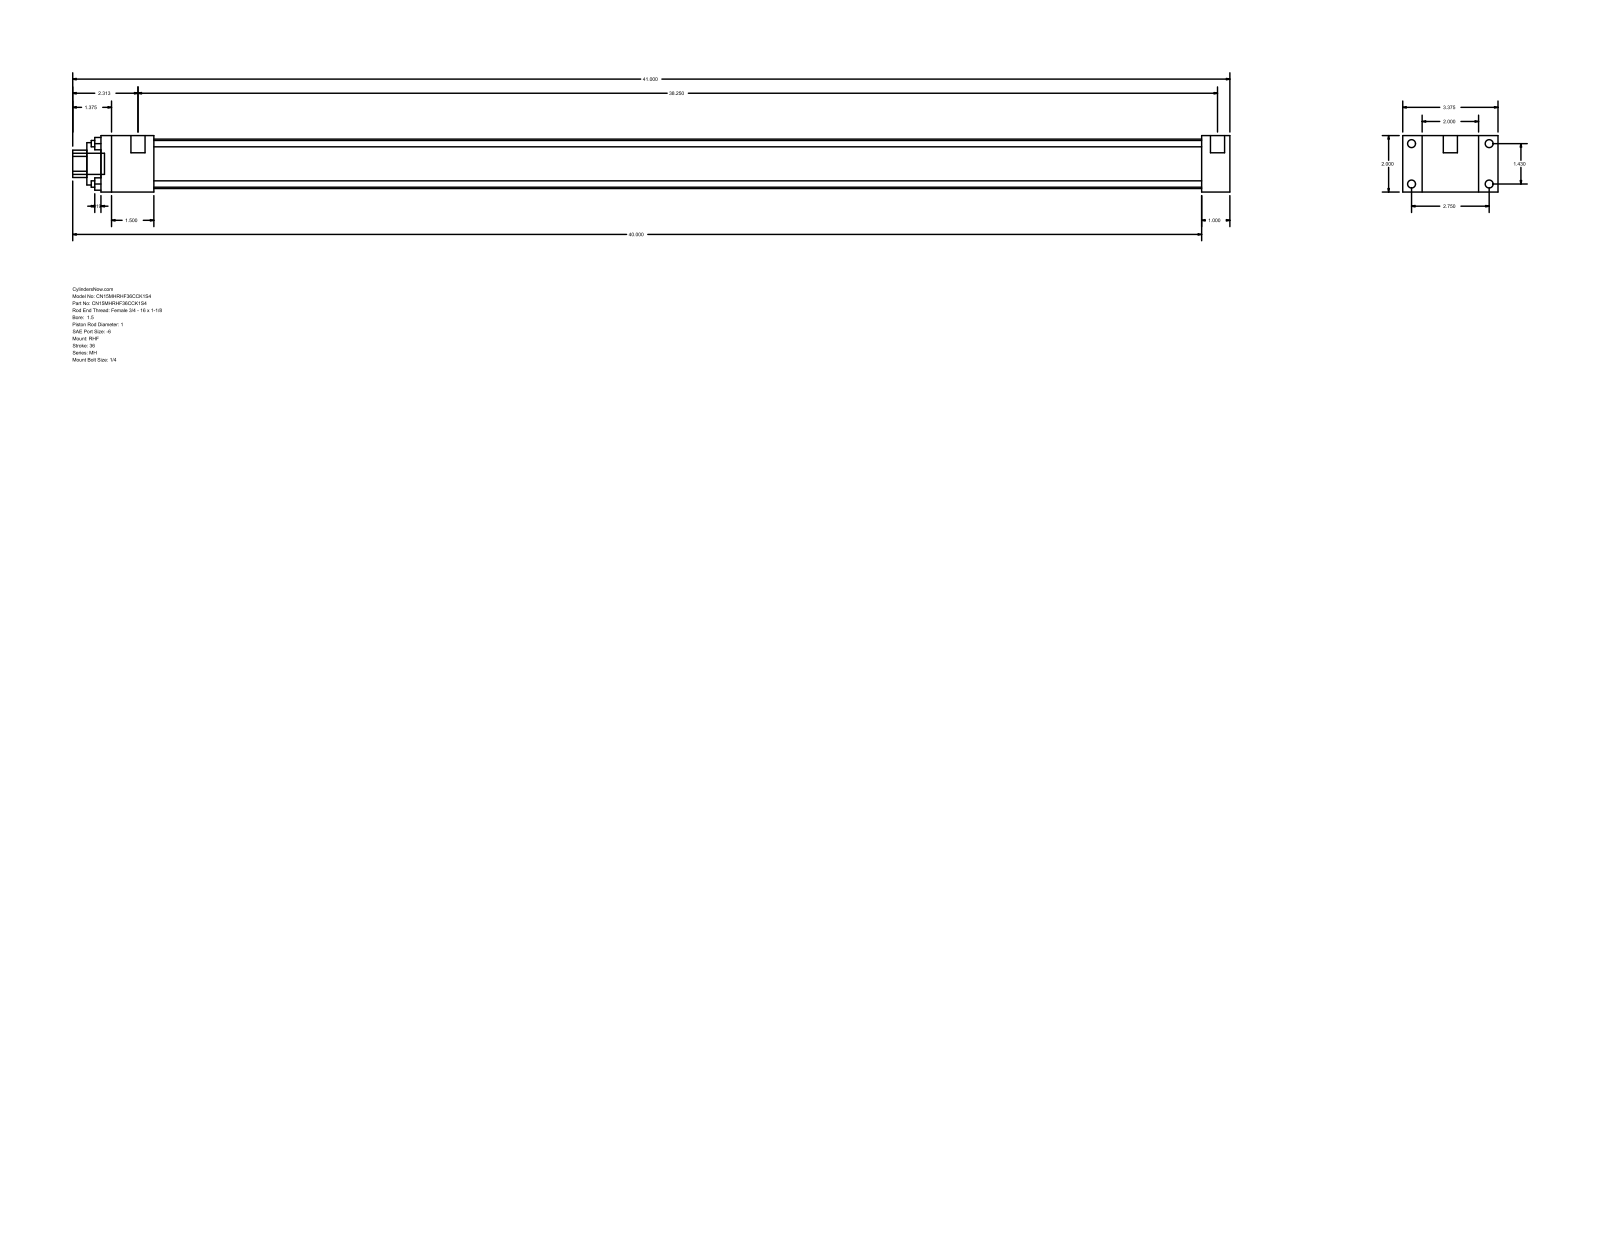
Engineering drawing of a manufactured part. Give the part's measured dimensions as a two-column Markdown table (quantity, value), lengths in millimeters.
| quantity | value |
| --- | --- |
| part name | MH_RHF__0150_1 |
| STEP written by | GSSL Pune (CONFIG_CONTROL_DESIGN) |
| units | millimeters |
| bodies | 0 solids, 88 faces (60 planar, 28 cylindrical, 0 other) |
| overall size | 1041.4 × 85.72 × 50.8 |
| round holes (diameter × count) | 5.71 × 4, 25.4 × 1, 38.1 × 1, 44.45 × 1 |
| round bosses / shafts (diameter × count) | 7.14 × 4, 5.56 × 4, 12.7 × 2, 19.05 × 1 |
| partial cylindrical surfaces (radius × count) | 12.29 × 1 |
| main face-to-face distances | 50.8, 25.4, 17.46, 68.26, 85.72, 1016, 990.6, 47.63, 942.97, 968.37 |
| hole center spacings | 25.68, 36.32, 51.36 |
